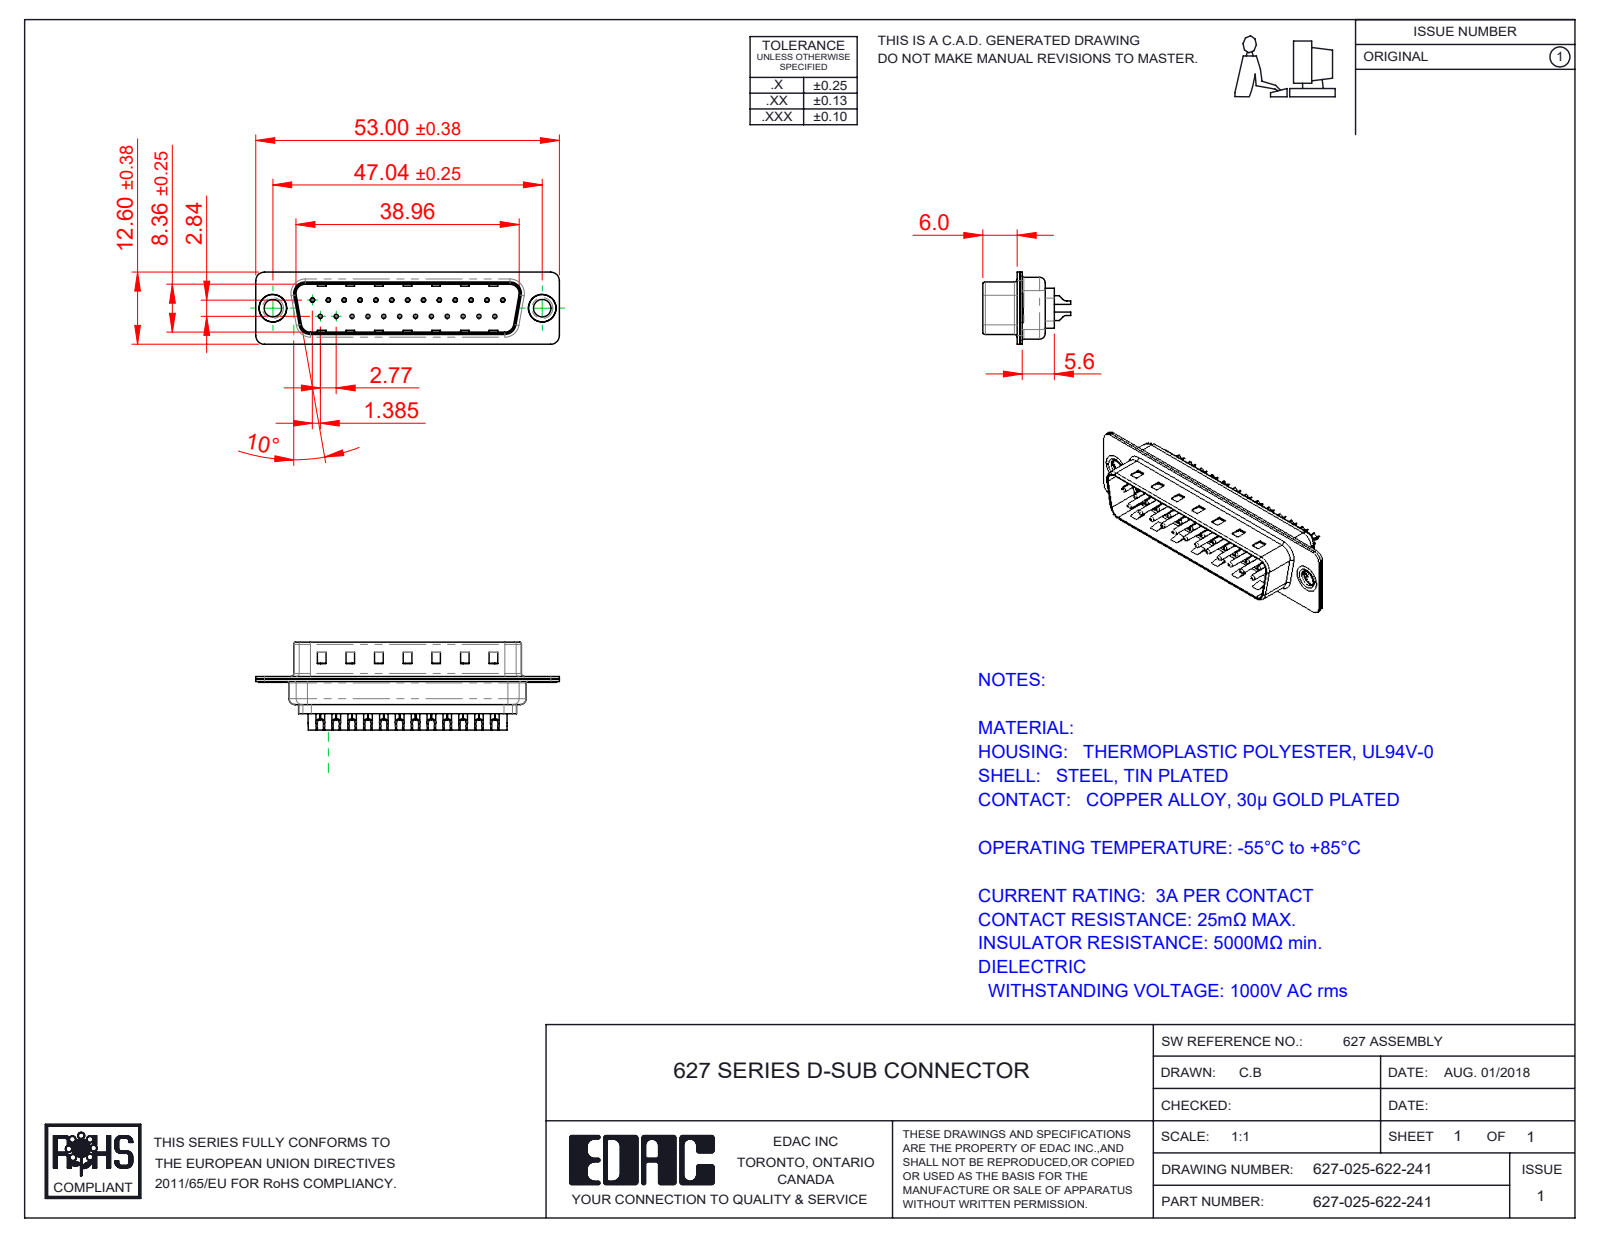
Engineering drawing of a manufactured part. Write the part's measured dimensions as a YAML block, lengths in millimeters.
part_name: "627 Housing_25 LP; 627 Shell Front_25 Contacts; 627-025-622-041; 627 Contact Row 1_22L (+3 more)"
step_written_by: "SolidWorks 2020 (CONFIG_CONTROL_DESIGN)"
units: millimeters
bodies: {solids: 30, faces: 1950, planar: 521, cylindrical: 846, other: 583}
overall_size: [53, 15.35, 12.6]
volume: 2613
surface_area: 7711
round_holes:
  - {diameter: 0.35, count: 25}
  - {diameter: 1.1, count: 25}
  - {diameter: 1.6, count: 25}
  - {diameter: 3.05, count: 2}
  - {diameter: 4, count: 2}
  - {diameter: 4.8, count: 2}
round_bosses_or_shafts:
  - {diameter: 2, count: 25}
  - {diameter: 1.5, count: 25}
  - {diameter: 0.75, count: 25}
  - {diameter: 5, count: 2}
  - {diameter: 4.9, count: 2}
  - {diameter: 3.55, count: 2}
partial_cylinders:
  - {radius: 1.5, count: 16}
  - {radius: 2, count: 12}
  - {radius: 0.5, count: 8}
  - {radius: 1.6, count: 8}
  - {radius: 1, count: 6}
  - {radius: 0.25, count: 4}
  - {radius: 0.6, count: 4}
  - {radius: 0.65, count: 4}
face_to_face_distances: [0.4, 0.45, 0.82, 9.58, 0.9, 8.76, 1.5, 1.4, 6.5, 6.05]
hole_center_spacings: [3.16, 8.31, 2.77, 5.54, 11.08, 16.62, 5.03, 5.04]
